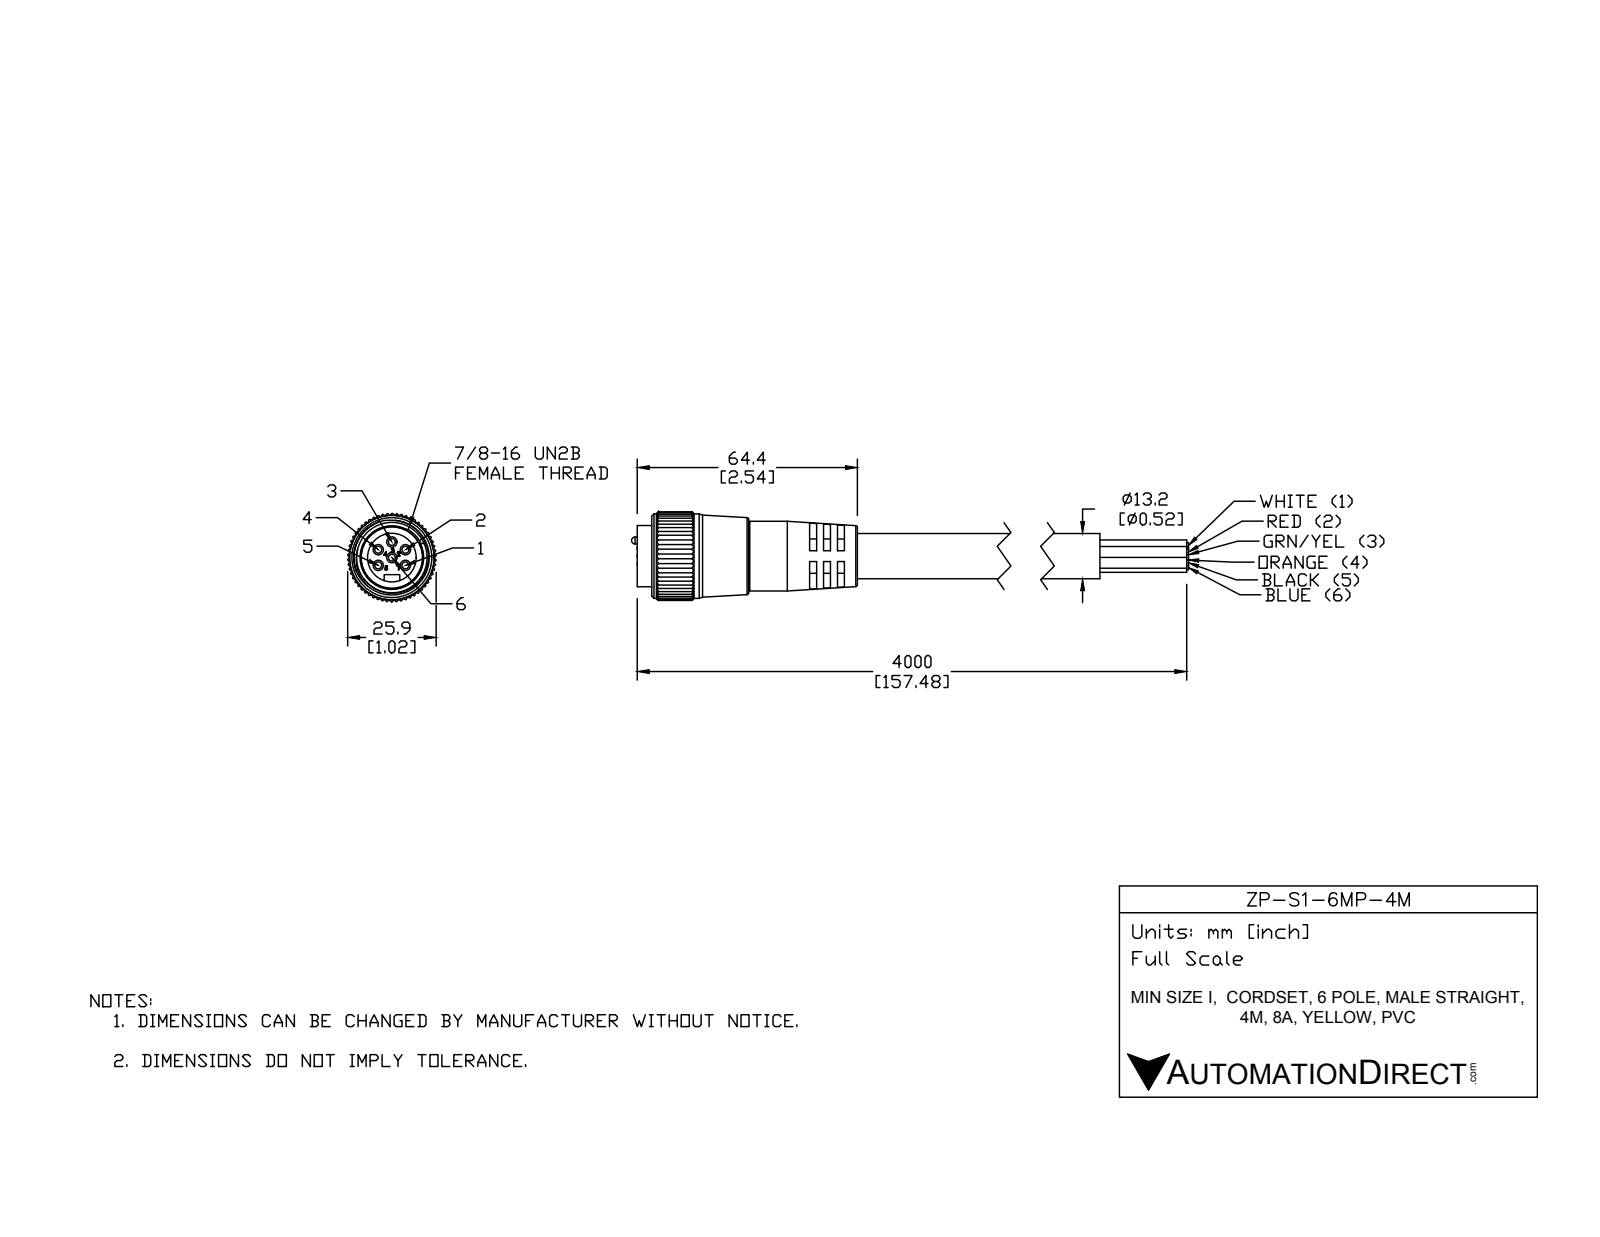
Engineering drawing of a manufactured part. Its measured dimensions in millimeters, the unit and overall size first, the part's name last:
Units: millimetres
Overall size (bounding box): 111.28 × 52.91 × 25.84
Round holes (diameter × count): ⌀14.22 ×1, ⌀19.96 ×1, ⌀20.45 ×1, ⌀21 ×1
Round bosses / shafts (diameter × count): ⌀3.05 ×6, ⌀2 ×6, ⌀13.21 ×2, ⌀24.68 ×1, ⌀20.4 ×1, ⌀19.5 ×1, ⌀17.88 ×1
Partial cylindrical surfaces — rounded edges, fillets, slot ends (radius × count): R0.25 ×165, R2.29 ×1, R5.25 ×1, R12.93 ×1
Main face-to-face distances: 2, 4.04, 2.04, 6.04, 2.02, 8.06, 6.06, 4.02, 4.03, 10.07
Volume: 31 376 mm³ · Surface area: 13 508 mm²
Bodies: 8 solids, 638 faces (229 planar, 326 cylindrical, 83 other)
Part name (STEP PRODUCT): ZP-S1-6MP-4M
STEP written by: SolidWorks 2015 (AUTOMOTIVE_DESIGN)
